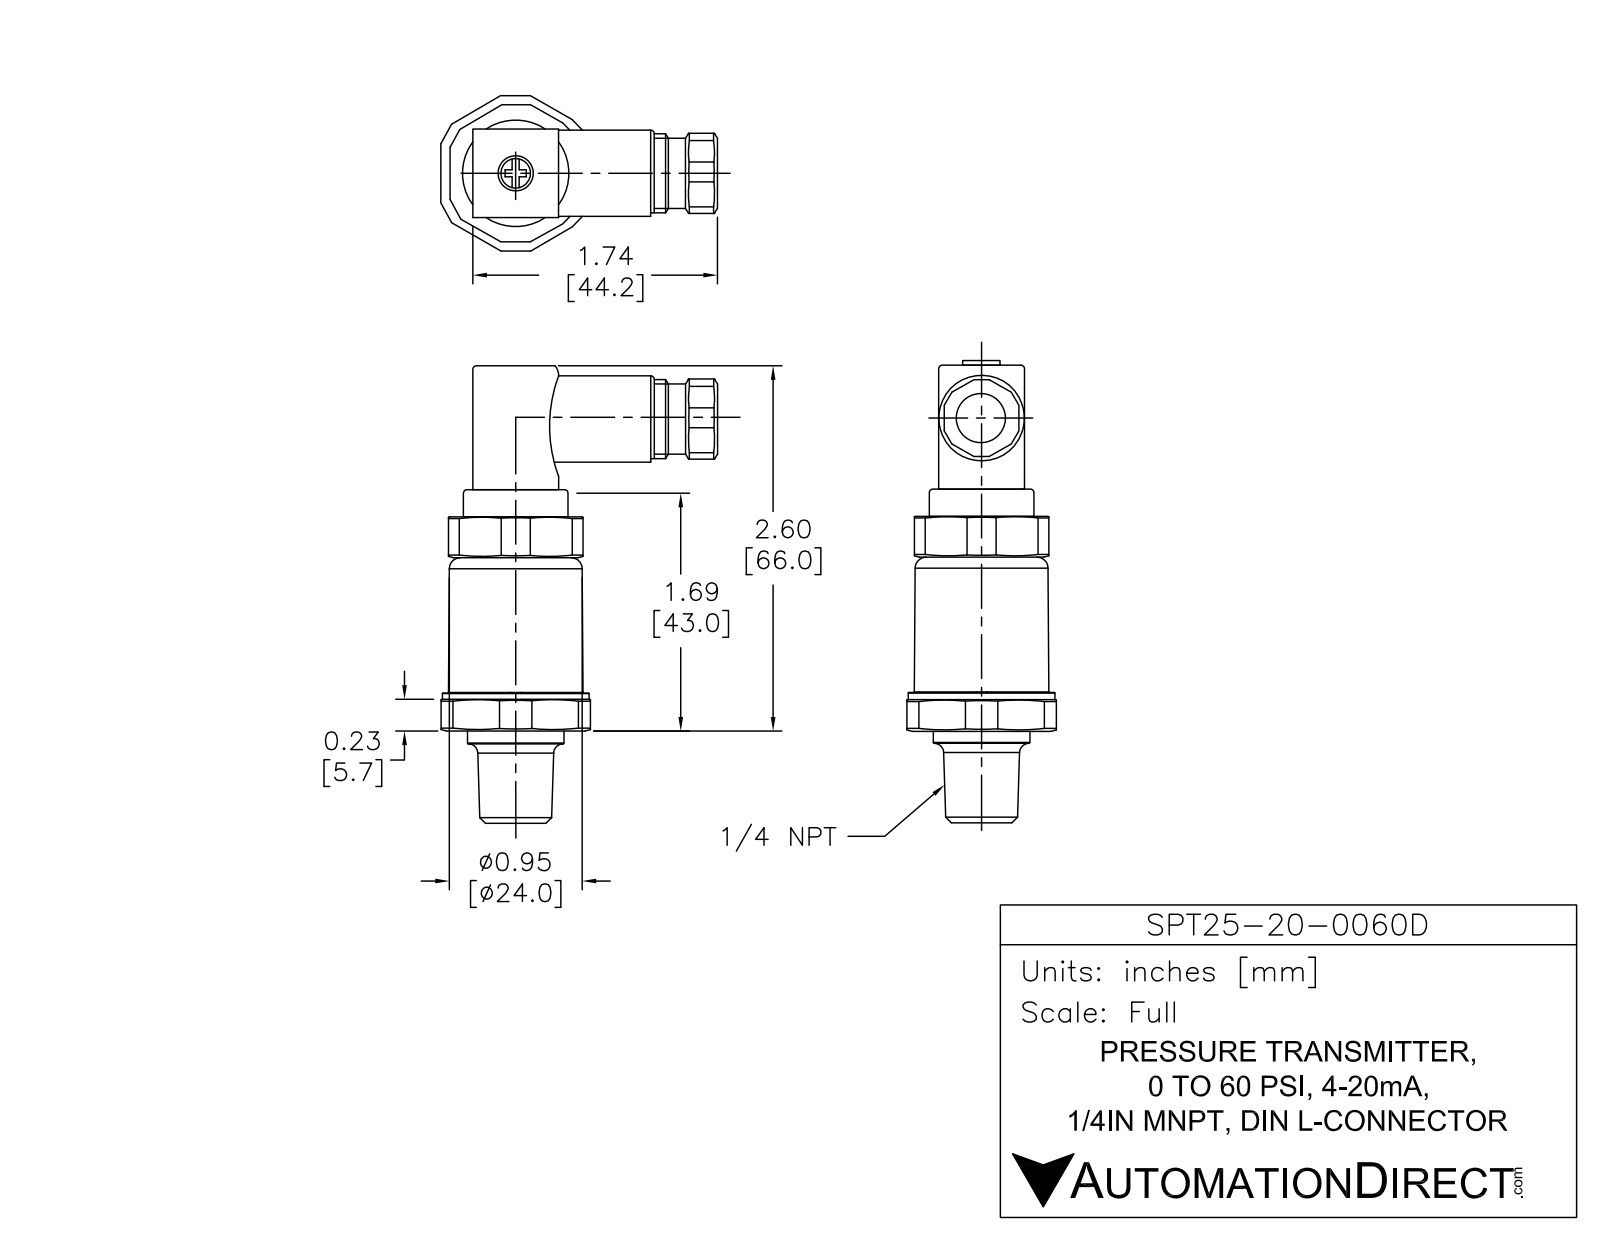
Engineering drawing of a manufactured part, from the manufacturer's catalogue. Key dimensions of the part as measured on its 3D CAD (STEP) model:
Part name (STEP PRODUCT): SPT25-20-0060D
STEP written by: SolidWorks 2011 (AUTOMOTIVE_DESIGN)
Units: millimetres
Bodies: 5 solids, 170 faces (96 planar, 64 cylindrical, 10 other)
Overall size (bounding box): 81.25 × 38.01 × 35.71
Volume: 27 900 mm³ · Surface area: 10 134 mm²
Round holes (diameter × count): ⌀1 ×1, ⌀3.3 ×1, ⌀7 ×1, ⌀8 ×1
Round bosses / shafts (diameter × count): ⌀26.75 ×1, ⌀24 ×1, ⌀17.5 ×1, ⌀15 ×1, ⌀14 ×1, ⌀11 ×1
Partial cylindrical surfaces — rounded edges, fillets, slot ends (radius × count): R1.5 ×8, R1.15 ×4, R2.25 ×4, R2 ×3, R1.15 ×1, R1.17 ×1, R14.5 ×1
Main face-to-face distances: 1.5, 29.5, 31, 15.75, 0.35, 15.4, 6.75, 37.75, 36.25, 5
Hole centre spacings: 1.33
